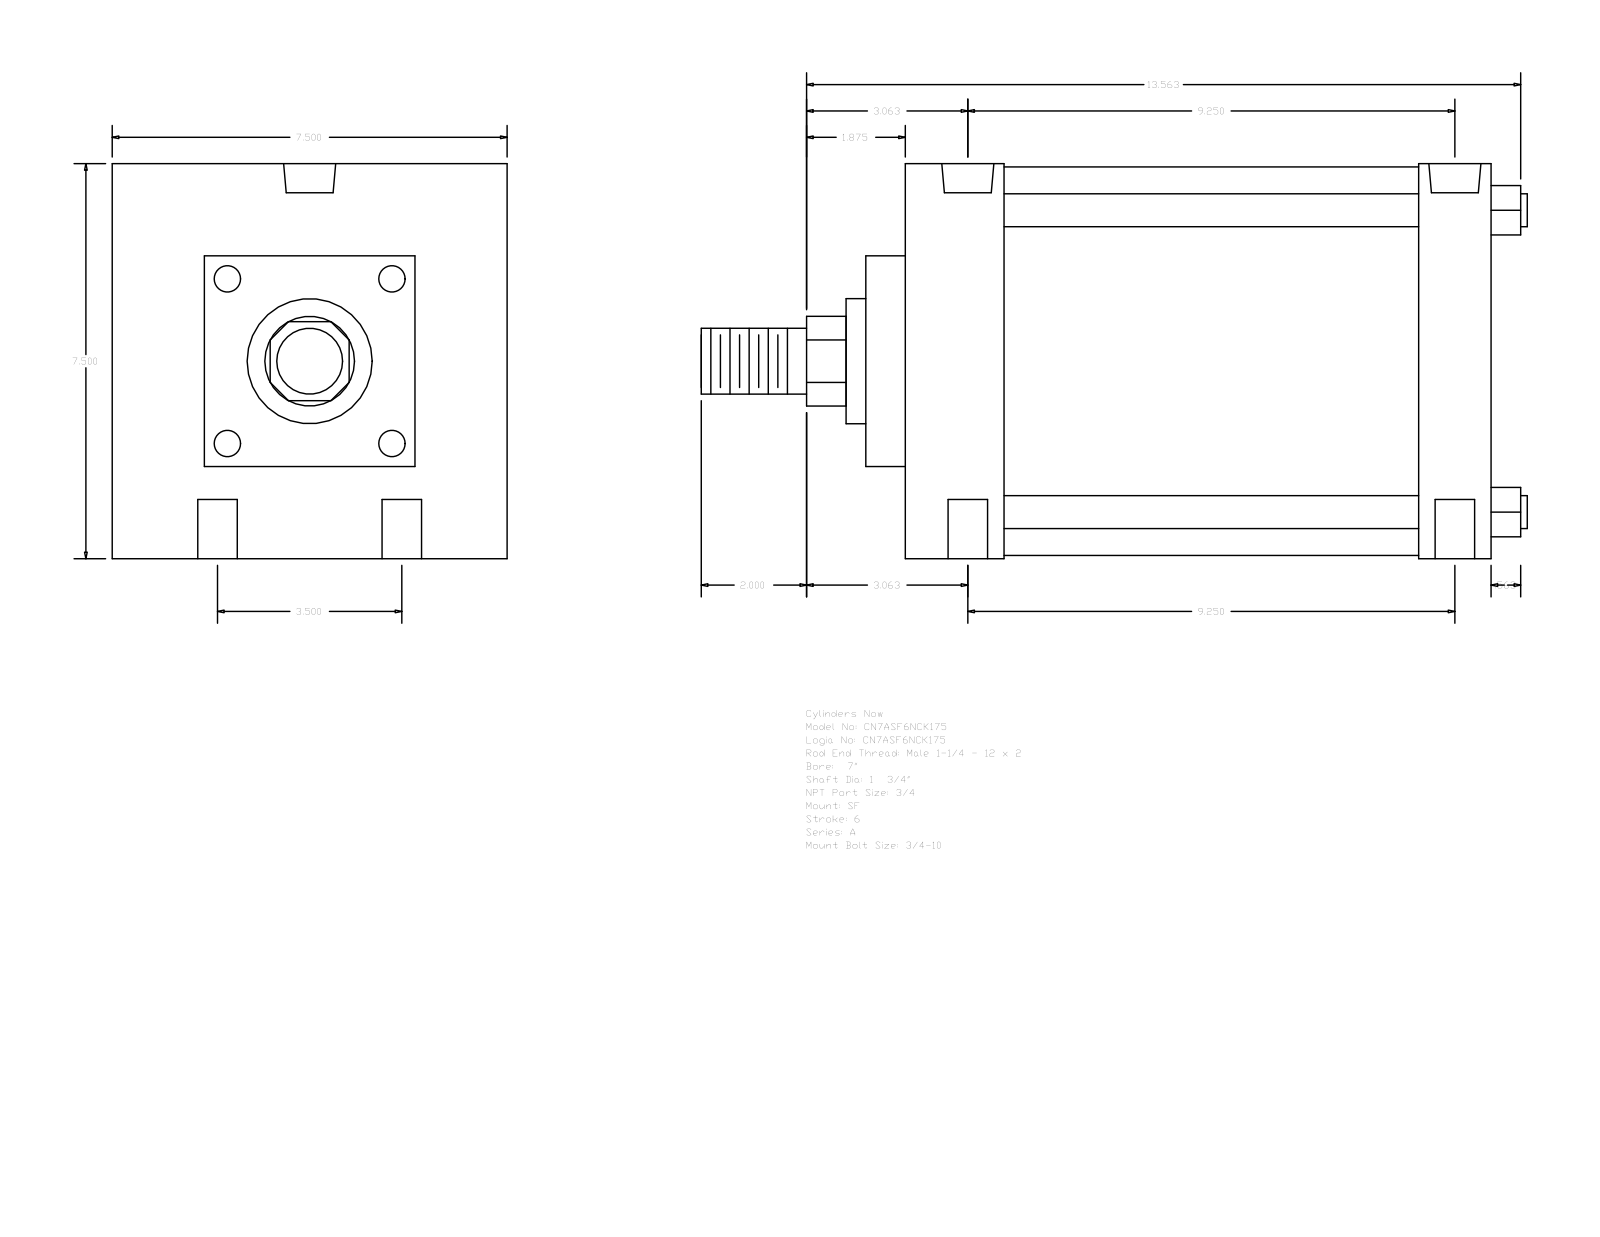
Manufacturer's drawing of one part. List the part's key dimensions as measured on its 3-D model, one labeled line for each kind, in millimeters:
Part name (STEP PRODUCT): A_SF__0700_1.75
STEP written by: GSSL Pune (CONFIG_CONTROL_DESIGN)
Units: millimetres
Bodies: 0 solids, 93 faces (67 planar, 26 cylindrical, 0 other)
Overall size (bounding box): 398.46 × 190.5 × 190.5
Round holes (diameter × count): ⌀19.05 ×4, ⌀15.08 ×2, ⌀25.12 ×2
Round bosses / shafts (diameter × count): ⌀15.88 ×4, ⌀187.32 ×1, ⌀60.33 ×1, ⌀44.45 ×1, ⌀31.75 ×1
Partial cylindrical surfaces — rounded edges, fillets, slot ends (radius × count): R21.63 ×1
Main face-to-face distances: 190.5, 282.58, 146.05, 19.05, 47.63, 247.65, 200.02, 234.95, 34.93, 44.45
Hole centre spacings: 44.45, 239.12, 234.95, 88.9, 251.21, 223.83
